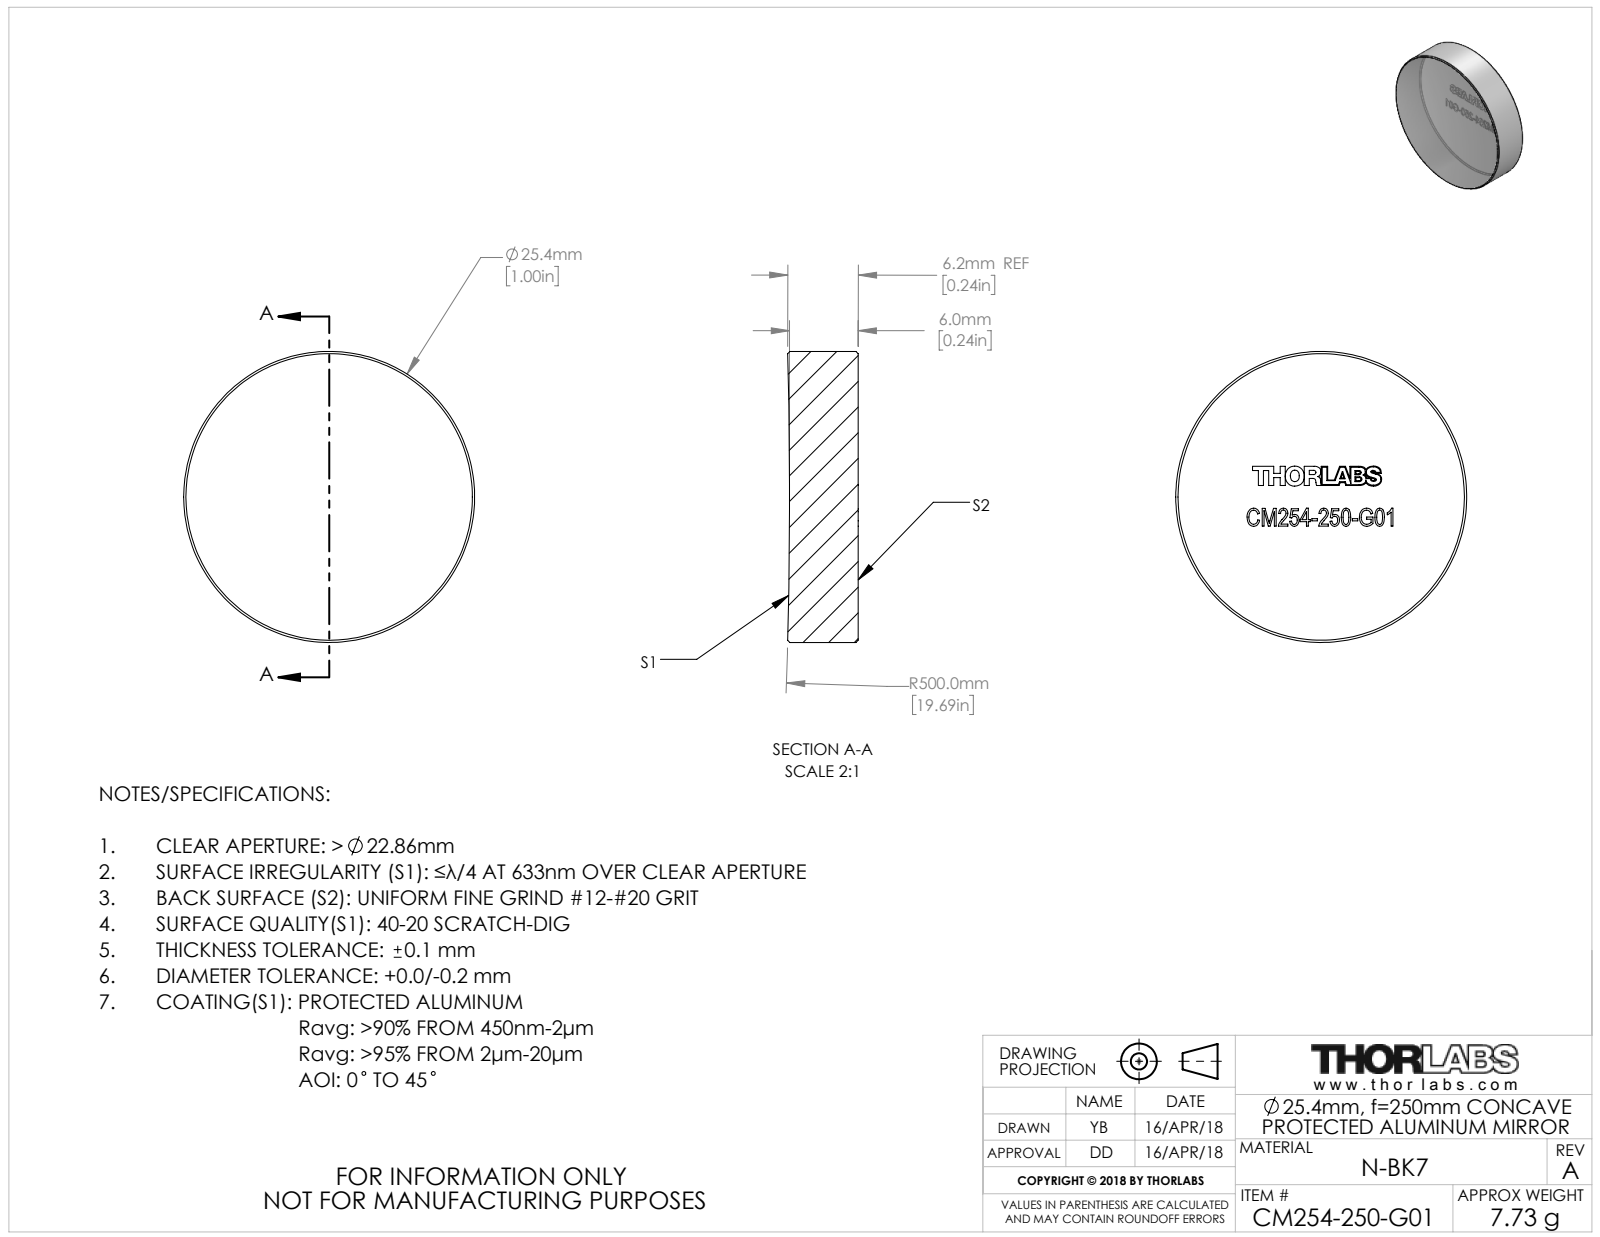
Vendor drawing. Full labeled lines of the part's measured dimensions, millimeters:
Part name (STEP PRODUCT): TTN153293-E0W
STEP written by: SolidWorks 2018 (CONFIG_CONTROL_DESIGN)
Units: millimetres
Bodies: 1 solid, 40 faces (32 planar, 2 cylindrical, 6 other)
Overall size (bounding box): 25.4 × 25.4 × 6.16
Volume: 3 078 mm³ · Surface area: 1 486 mm²
Round bosses / shafts (diameter × count): ⌀25.4 ×1
